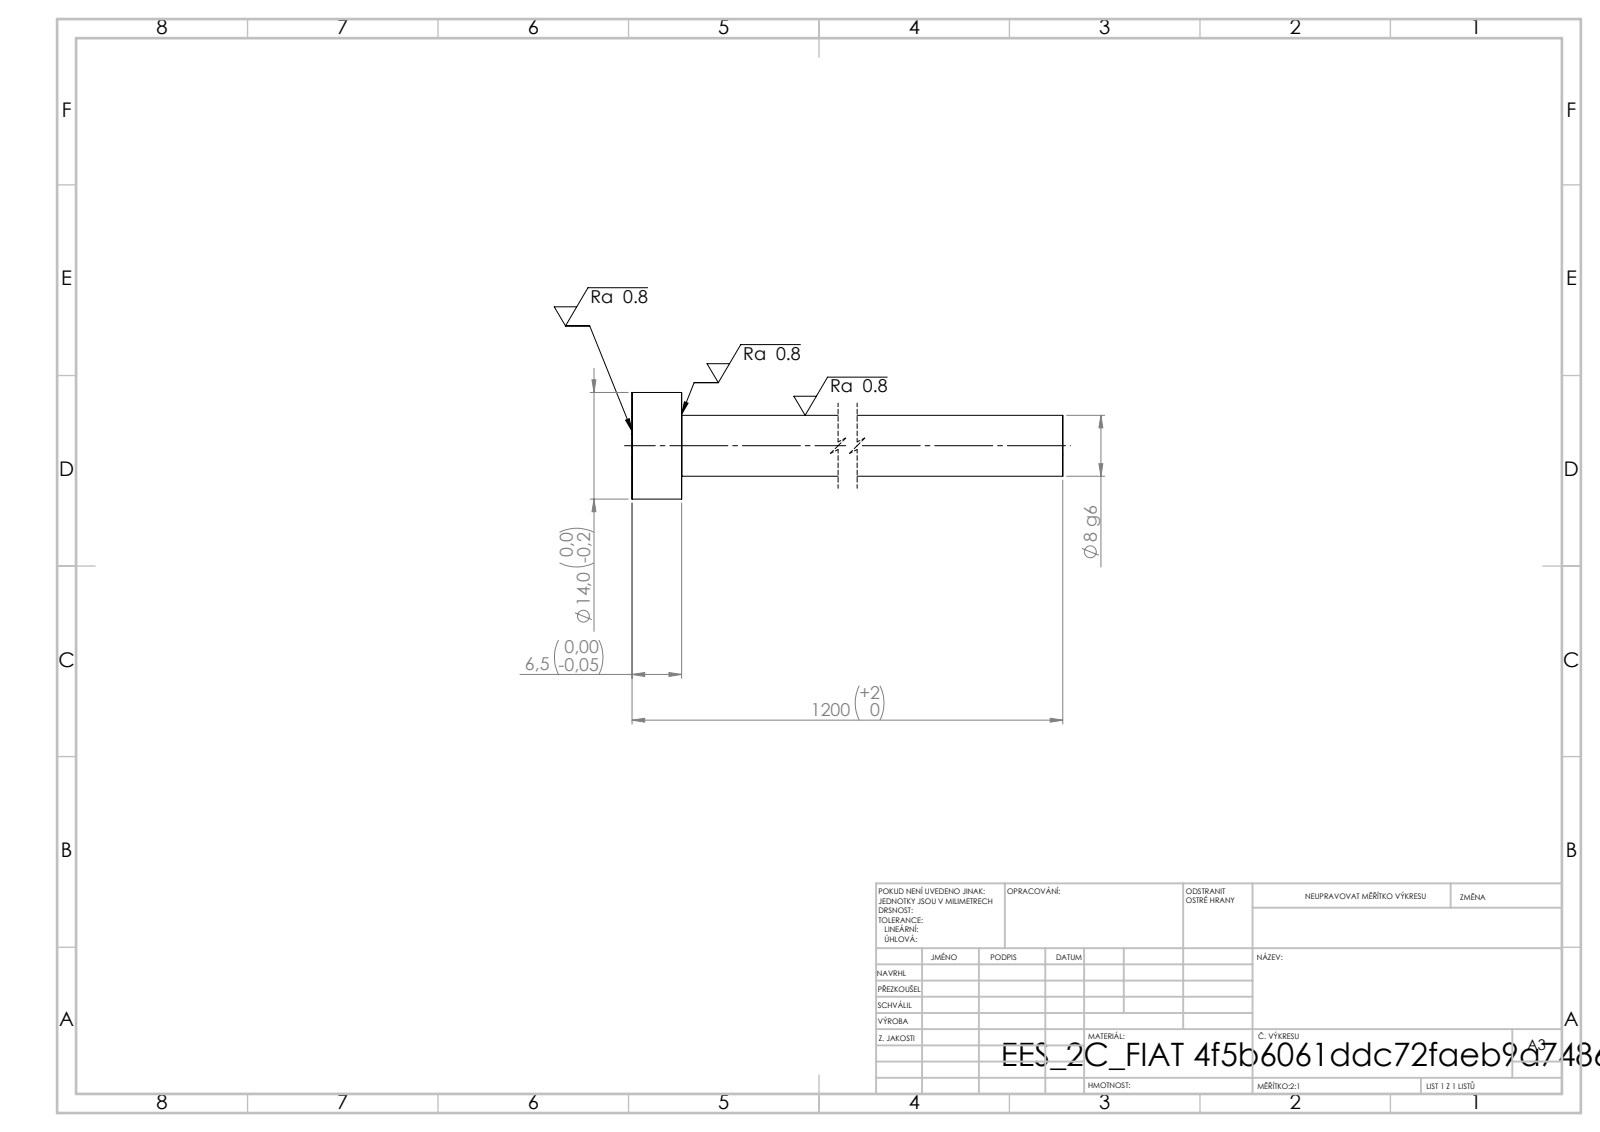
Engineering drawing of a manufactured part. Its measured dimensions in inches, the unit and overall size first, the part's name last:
Units: inches
Overall size (bounding box): 47.244 × 0.551 × 0.551
Round bosses / shafts (diameter × count): ⌀0.551 ×1, ⌀0.315 ×1
Main face-to-face distances: 0.256, 47.244, 46.988
Volume: 3.722 in³ · Surface area: 47.41 in²
Bodies: 1 solid, 7 faces (3 planar, 4 cylindrical, 0 other)
STEP written by: SolidWorks 2019 (CONFIG_CONTROL_DESIGN)
